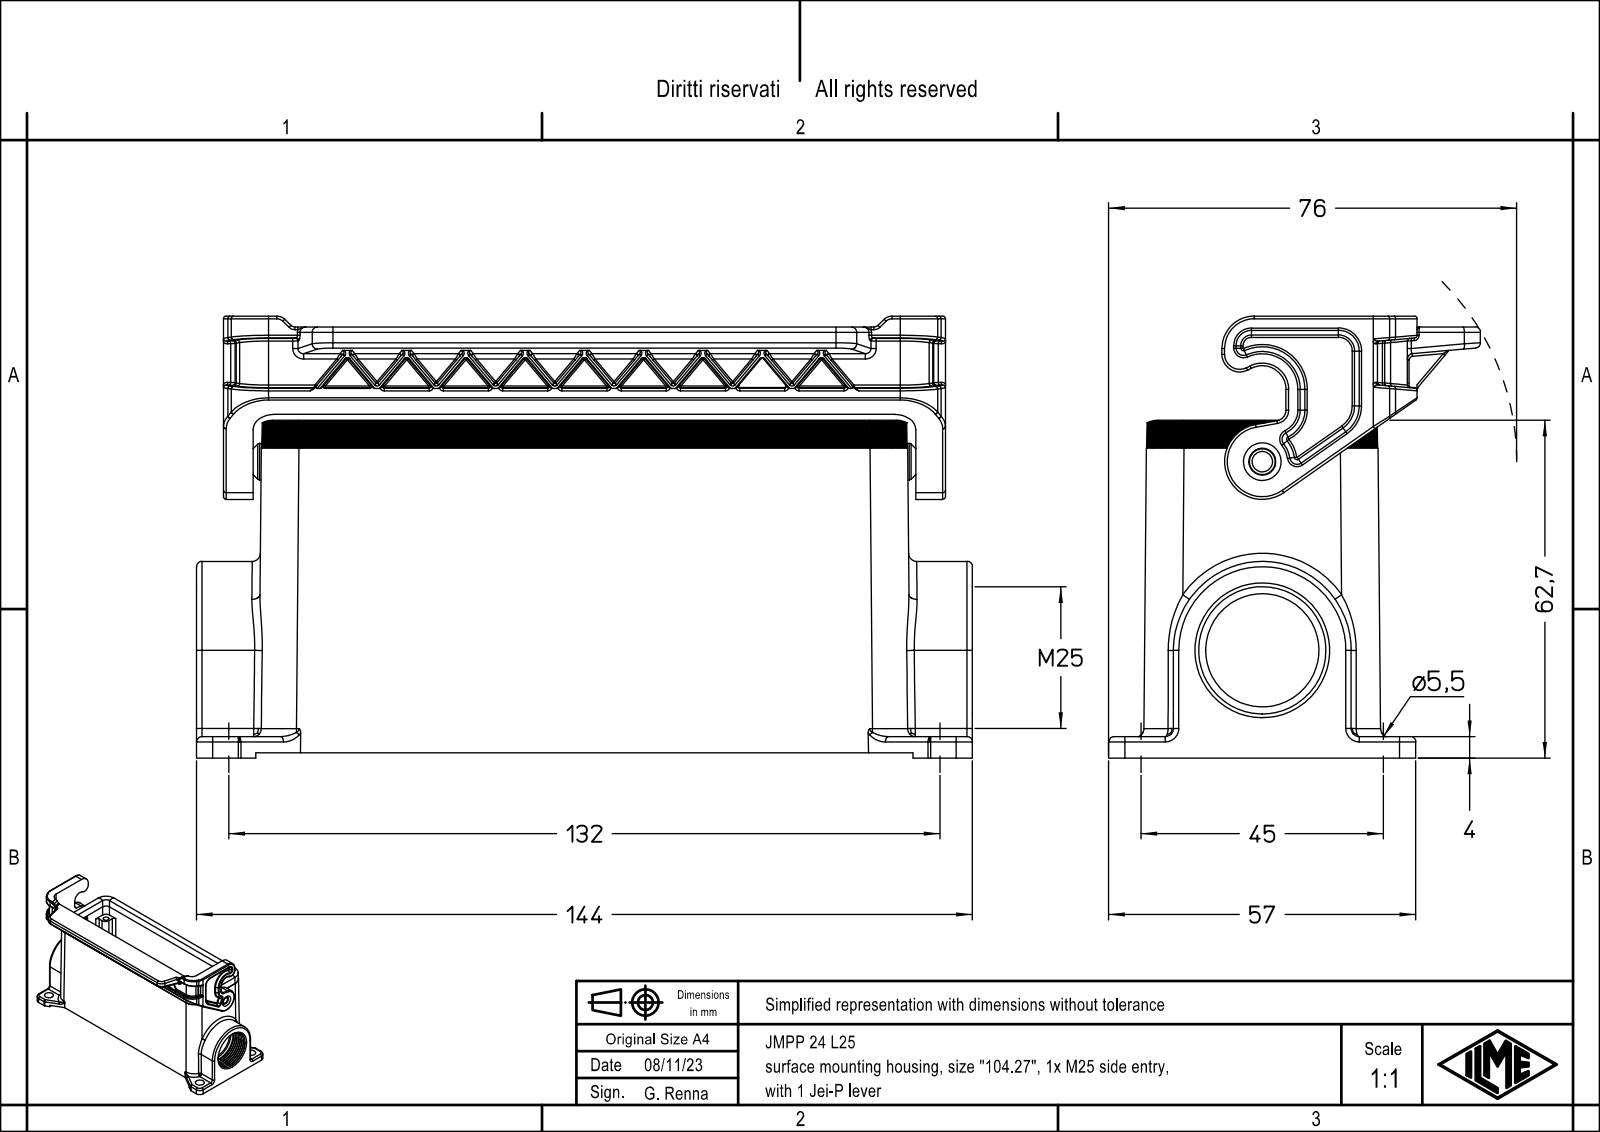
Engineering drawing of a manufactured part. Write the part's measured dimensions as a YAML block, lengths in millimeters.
part_name: "JMPP 24 L25"
step_written_by: "Creo Elements/Direct Modeling 20.1B 02-Apr-2019 (C) Parametric Technology GmbH (AUTOMOTIVE_DESIGN)"
units: millimeters
bodies: {solids: 1, faces: 928, planar: 197, cylindrical: 384, other: 347}
overall_size: [144, 82, 69]
volume: 139623
surface_area: 65855
round_holes:
  - {diameter: 3, count: 4}
  - {diameter: 3.5, count: 4}
  - {diameter: 5.5, count: 4}
  - {diameter: 4.8, count: 1}
  - {diameter: 21, count: 1}
  - {diameter: 23.6, count: 1}
round_bosses_or_shafts:
  - {diameter: 6.8, count: 1}
partial_cylinders:
  - {radius: 0.3, count: 126}
  - {radius: 0.5, count: 77}
  - {radius: 1, count: 27}
  - {radius: 3, count: 16}
  - {radius: 1.5, count: 12}
  - {radius: 2, count: 9}
  - {radius: 7, count: 9}
  - {radius: 4, count: 8}
face_to_face_distances: [3, 1, 79, 76, 4, 7, 10.5, 133.5, 80, 38.9]
hole_center_spacings: [16.64, 38.63, 118.34, 123.37, 27, 45, 104, 107.45]
